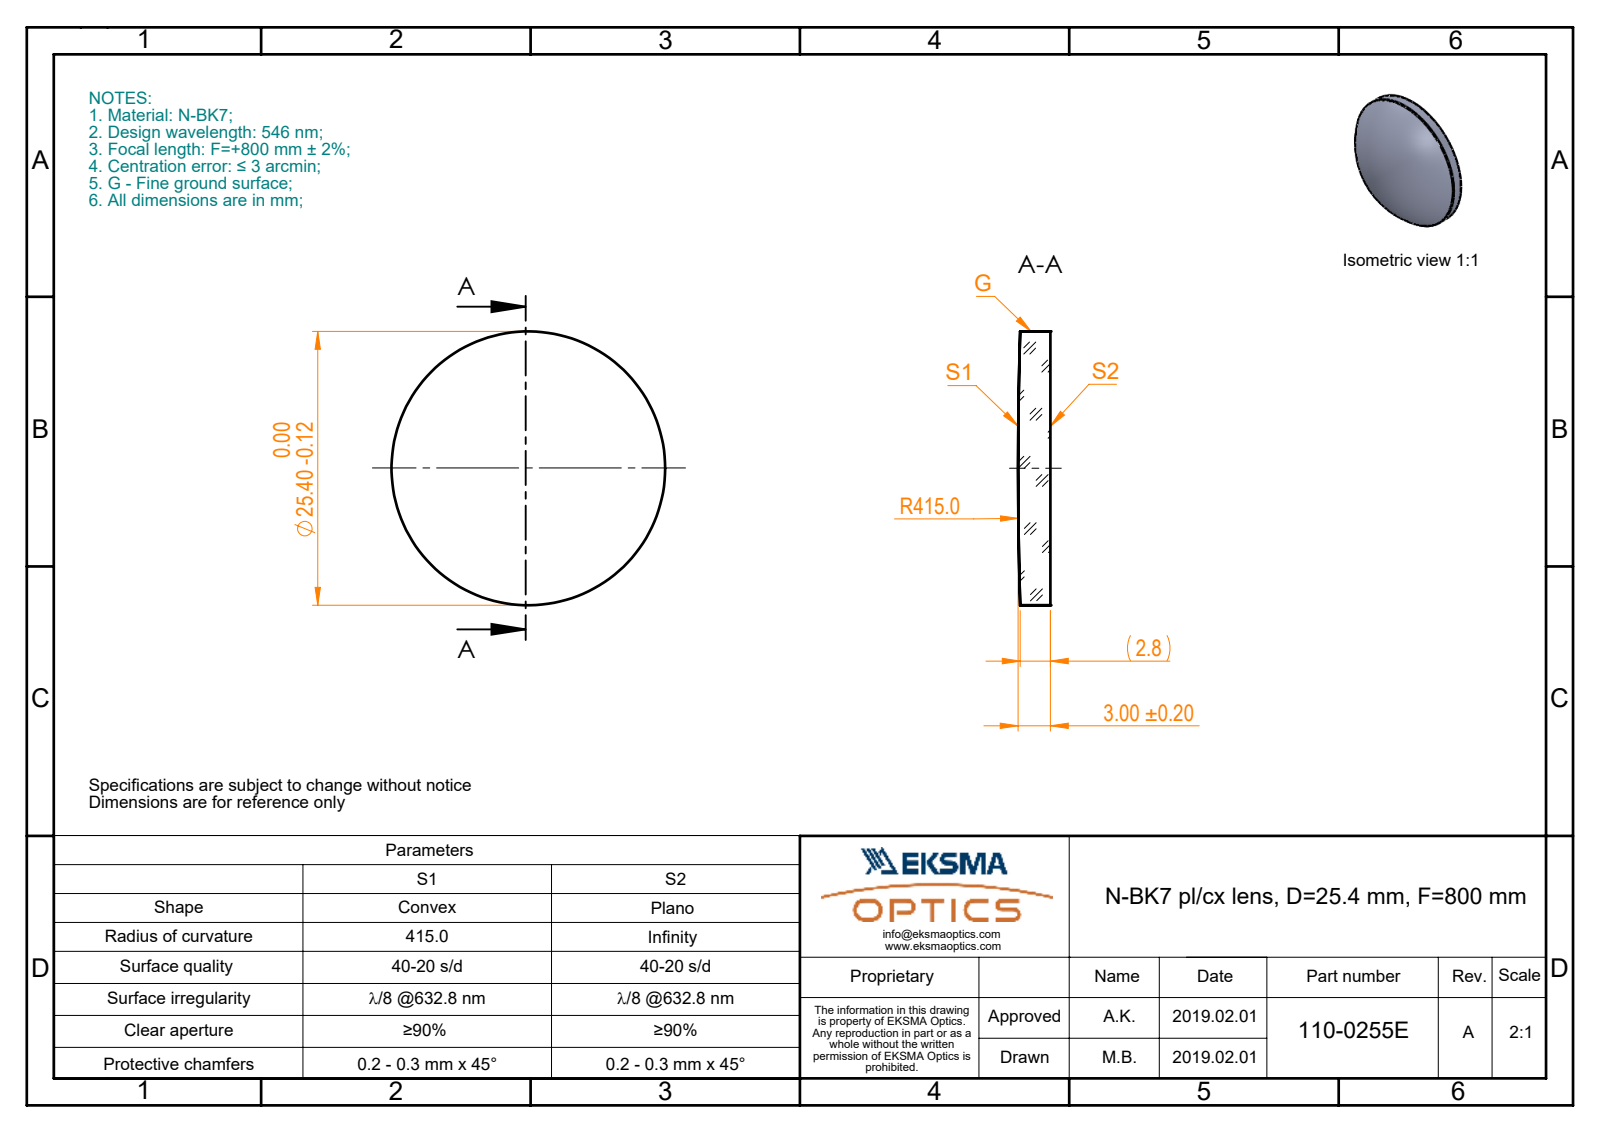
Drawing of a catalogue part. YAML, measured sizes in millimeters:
part_name: "110-0255E BK7 pl-cx 25.4 F800"
step_written_by: "SolidWorks 2017 (CONFIG_CONTROL_DESIGN)"
units: millimeters
bodies: {solids: 1, faces: 5, planar: 1, cylindrical: 2, other: 2}
overall_size: [25.4, 25.4, 3]
volume: 1471
surface_area: 1237
round_bosses_or_shafts:
  - {diameter: 25.4, count: 1}
